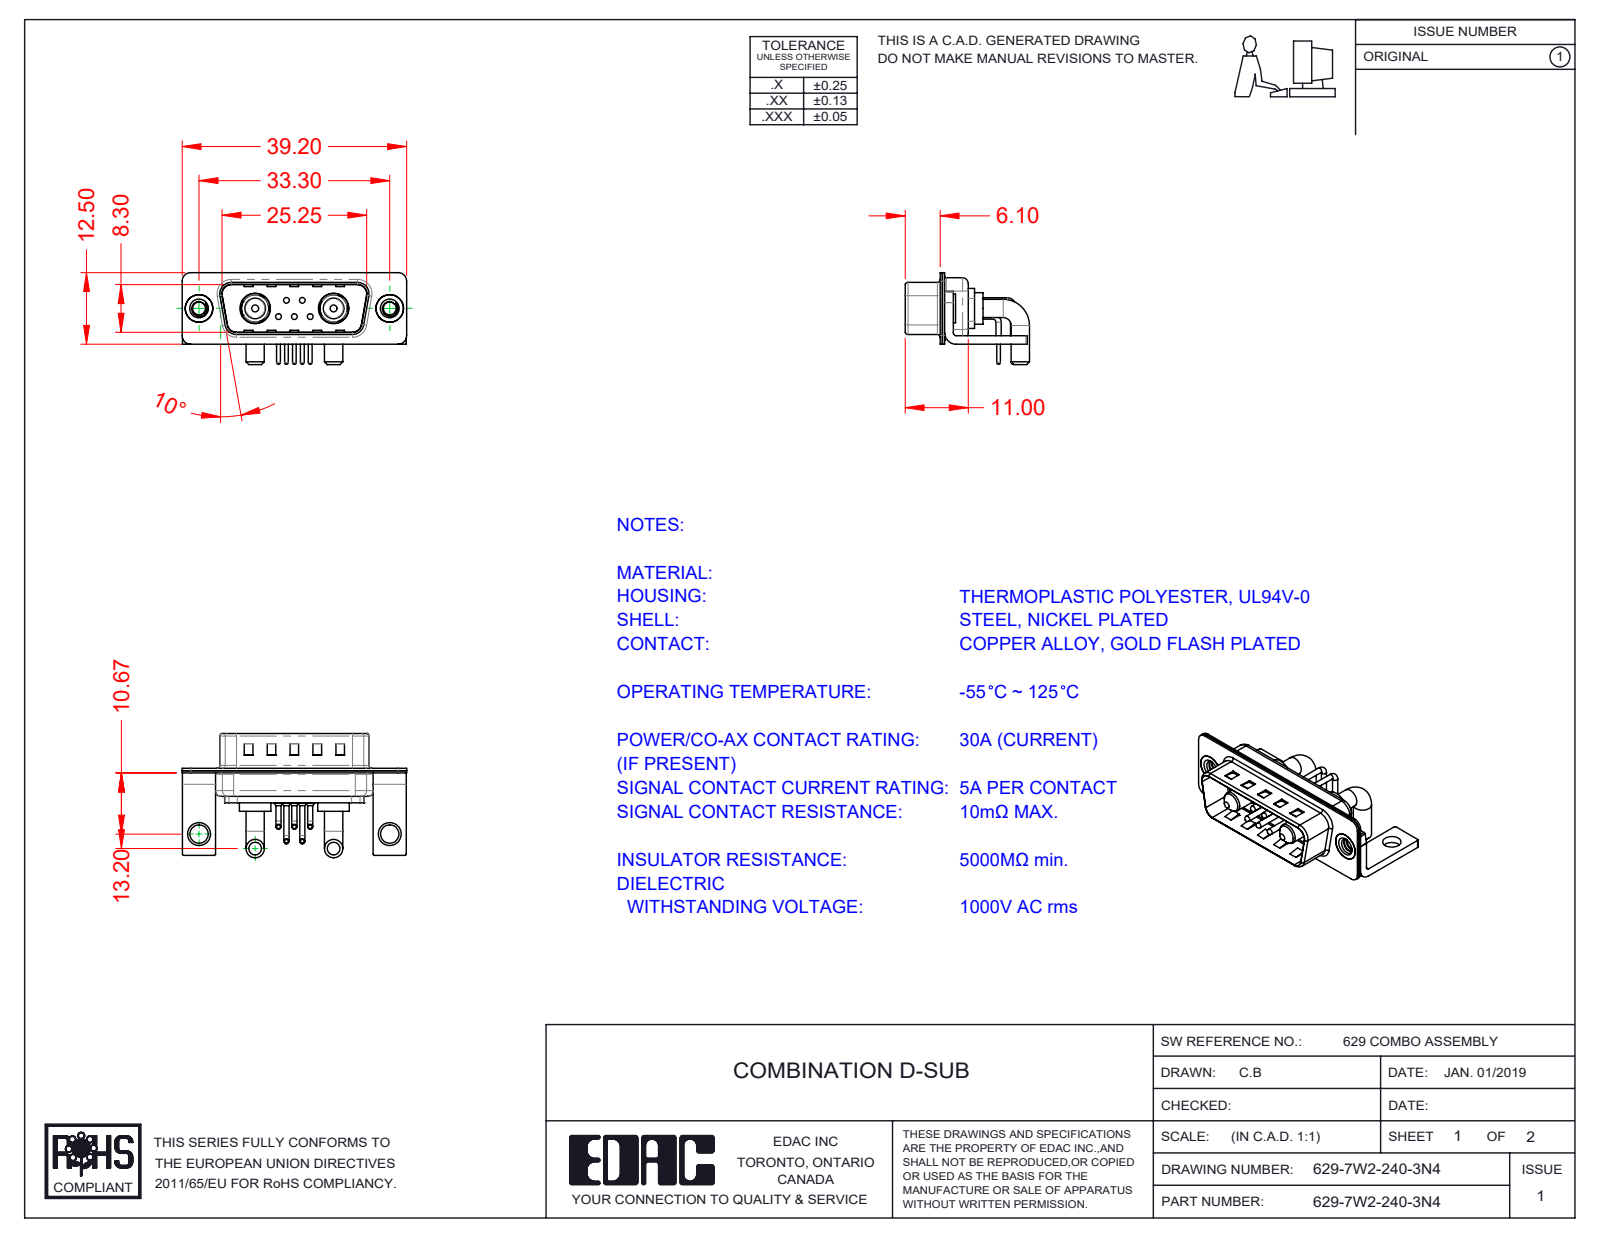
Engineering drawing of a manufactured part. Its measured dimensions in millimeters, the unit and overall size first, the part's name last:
Units: millimetres
Overall size (bounding box): 39.2 × 21.7 × 16.05
Round holes (diameter × count): ⌀0.75 ×5, ⌀1.6 ×5, ⌀2 ×5, ⌀2.26 ×2, ⌀3.2 ×2, ⌀4 ×2, ⌀4.8 ×2, ⌀4.85 ×2, ⌀5.3 ×2
Round bosses / shafts (diameter × count): ⌀0.9 ×10, ⌀1.5 ×5, ⌀1 ×5, ⌀0.65 ×5, ⌀3.2 ×4, ⌀5.5 ×2, ⌀5.2 ×2, ⌀5 ×2
Partial cylindrical surfaces — rounded edges, fillets, slot ends (radius × count): R0.25 ×16, R1.5 ×16, R2 ×13, R0.5 ×9, R1.6 ×8, R1.01 ×5, R0.6 ×4, R0.65 ×4
Main face-to-face distances: 0.4, 0.8, 1.5, 9.5, 9.1, 8.7, 9.9, 0.6, 5.2, 0.75
Hole centre spacings: 3.16, 2.77, 9.8, 23.5, 33.3, 4.31, 4.33, 5.03
Volume: 2 478 mm³ · Surface area: 5 718 mm²
Bodies: 16 solids, 1016 faces (499 planar, 373 cylindrical, 144 other)
Part name (STEP PRODUCT): 629Combo Stabilizer Bracket; 629Combo Housing_7W2; 629Combo Contact Row 1; 629-7W2-240-3N4 (+5 more)
STEP written by: SolidWorks 2020 (CONFIG_CONTROL_DESIGN)
